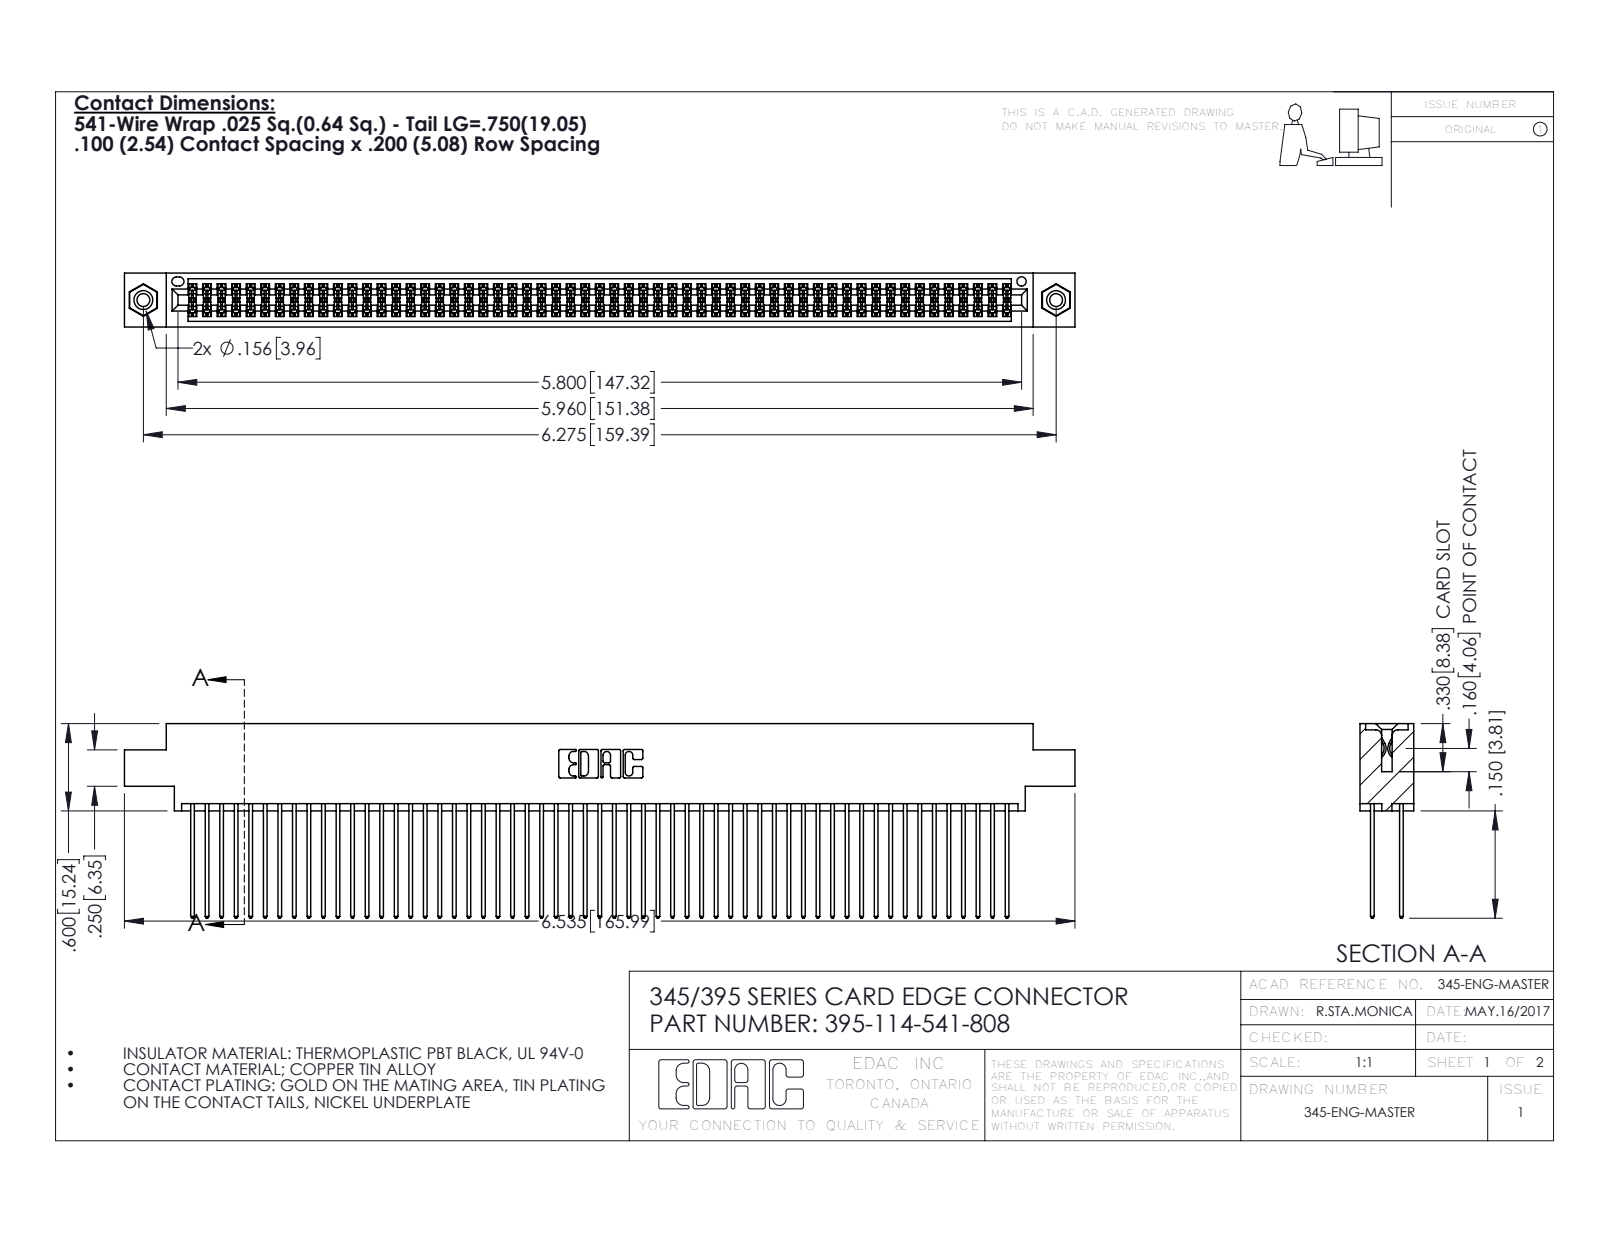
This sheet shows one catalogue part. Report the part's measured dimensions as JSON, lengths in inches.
{"part_name": "395-114-541-808; 345 Part_0.170 Offset - 0.156 Dia-TI; 345-250-001_345-250-003-102; 345-292-001_345-293-141", "step_written_by": "SolidWorks 2016 (CONFIG_CONTROL_DESIGN)", "units": "inches", "bodies": {"solids": 117, "faces": 5890, "planar": 3878, "cylindrical": 1996, "other": 16}, "overall_size": [6.535, 1.337, 0.37], "volume_in3": 1.025, "surface_area_in2": 43.95, "round_holes": [[0.089, 2], [0.125, 2], [0.156, 2], [0.064, 1]], "round_bosses_or_shafts": [[0.155, 2]], "partial_cylinders_radius": [[0.006, 171], [0.01, 114], [0.01, 22], [0.007, 6], [0.031, 6], [0.026, 3], [0.014, 2], [0.019, 2]], "face_to_face_distances": [0.072, 0.298, 0.2, 0.098, 0.272, 0.025, 0.225, 0.37, 0.175, 0.149], "hole_center_spacings": [0.27, 6.039, 6.275]}
